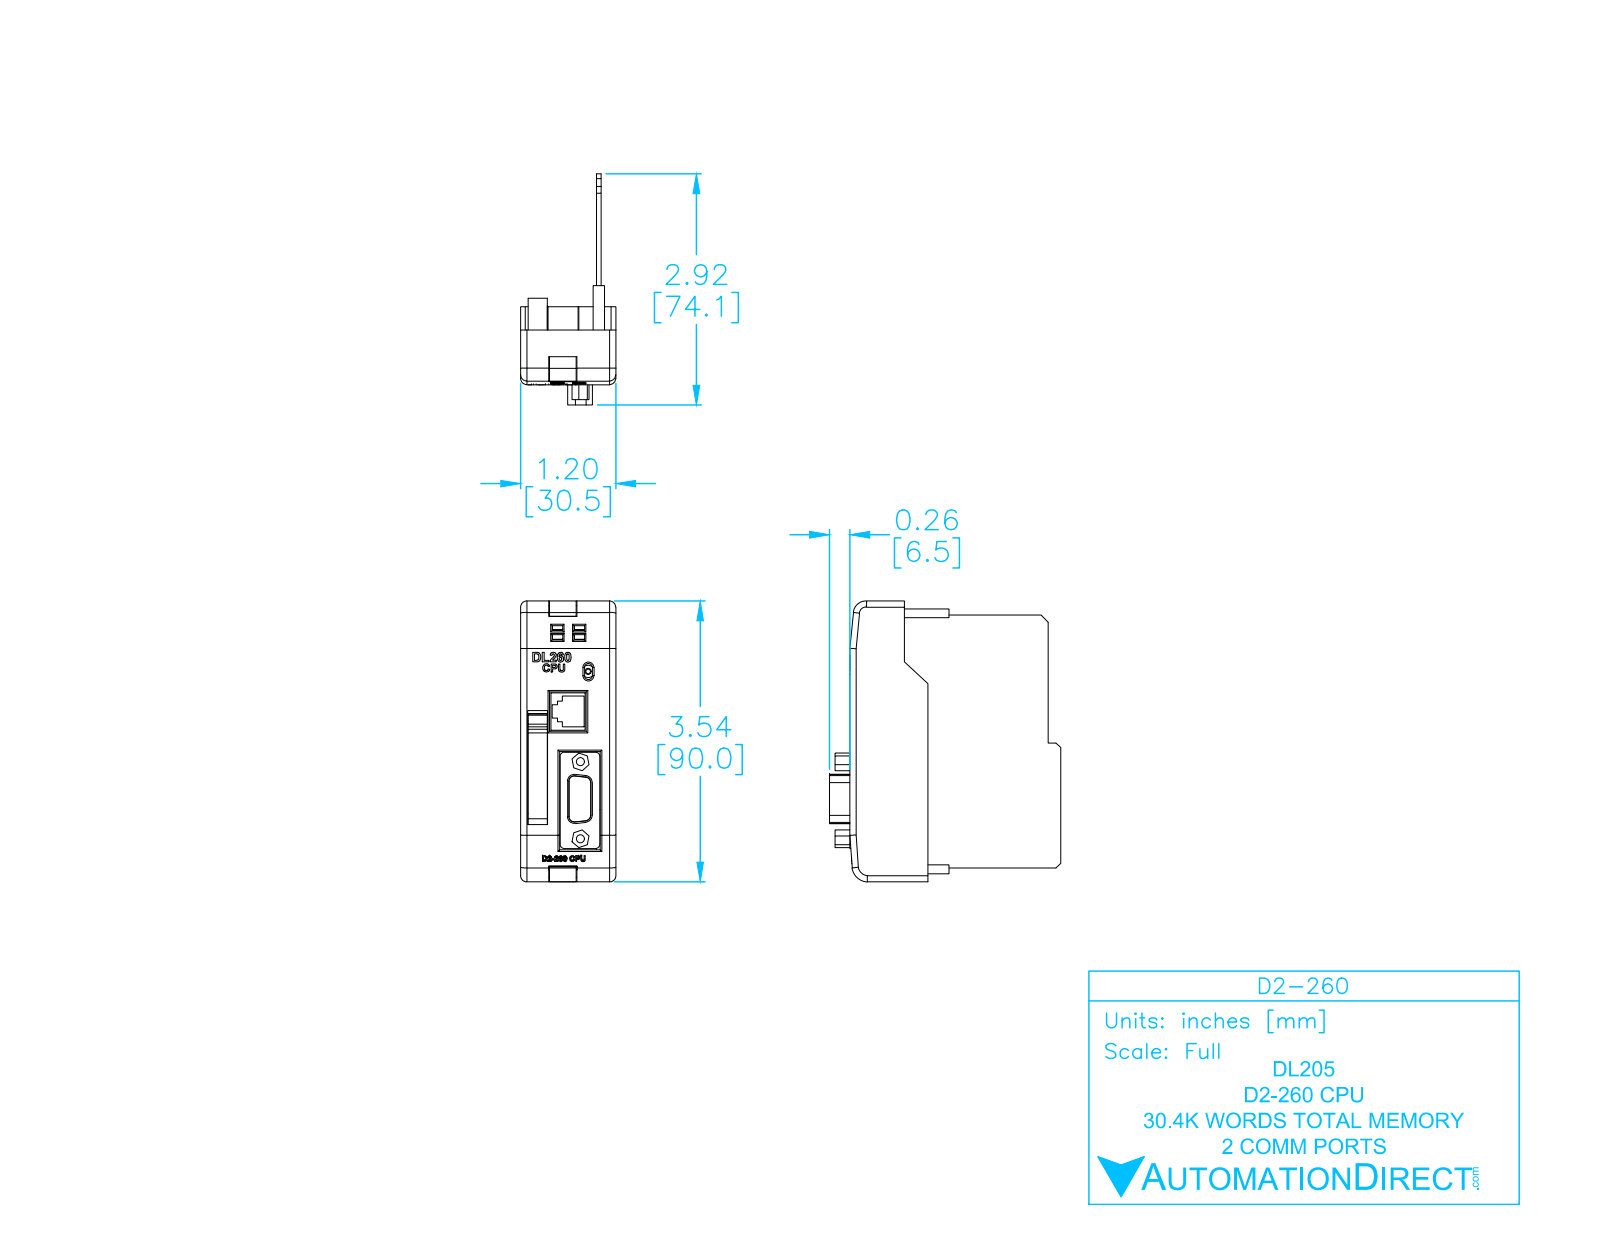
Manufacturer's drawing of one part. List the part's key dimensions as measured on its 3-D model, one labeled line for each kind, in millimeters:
Part name (STEP PRODUCT): D2-260
STEP written by: SolidWorks 2009 (AUTOMOTIVE_DESIGN)
Units: millimetres
Bodies: 6 solids, 607 faces (343 planar, 108 cylindrical, 156 other)
Overall size (bounding box): 90 × 74.07 × 30.5
Volume: 24 901 mm³ · Surface area: 33 750 mm²
Round holes (diameter × count): ⌀2.5 ×2
Round bosses / shafts (diameter × count): ⌀4 ×1, ⌀2 ×1, ⌀1.5 ×1
Partial cylindrical surfaces — rounded edges, fillets, slot ends (radius × count): R0.5 ×33, R2 ×10, R1.75 ×8, R0.25 ×4, R1.5 ×4, R2.25 ×4, R1.25 ×2, R0.42 ×1
Main face-to-face distances: 1.5, 24.28, 4.72, 29, 25.78, 30.5, 6.22, 22.78, 27.5, 3.22
Hole centre spacings: 24.67
